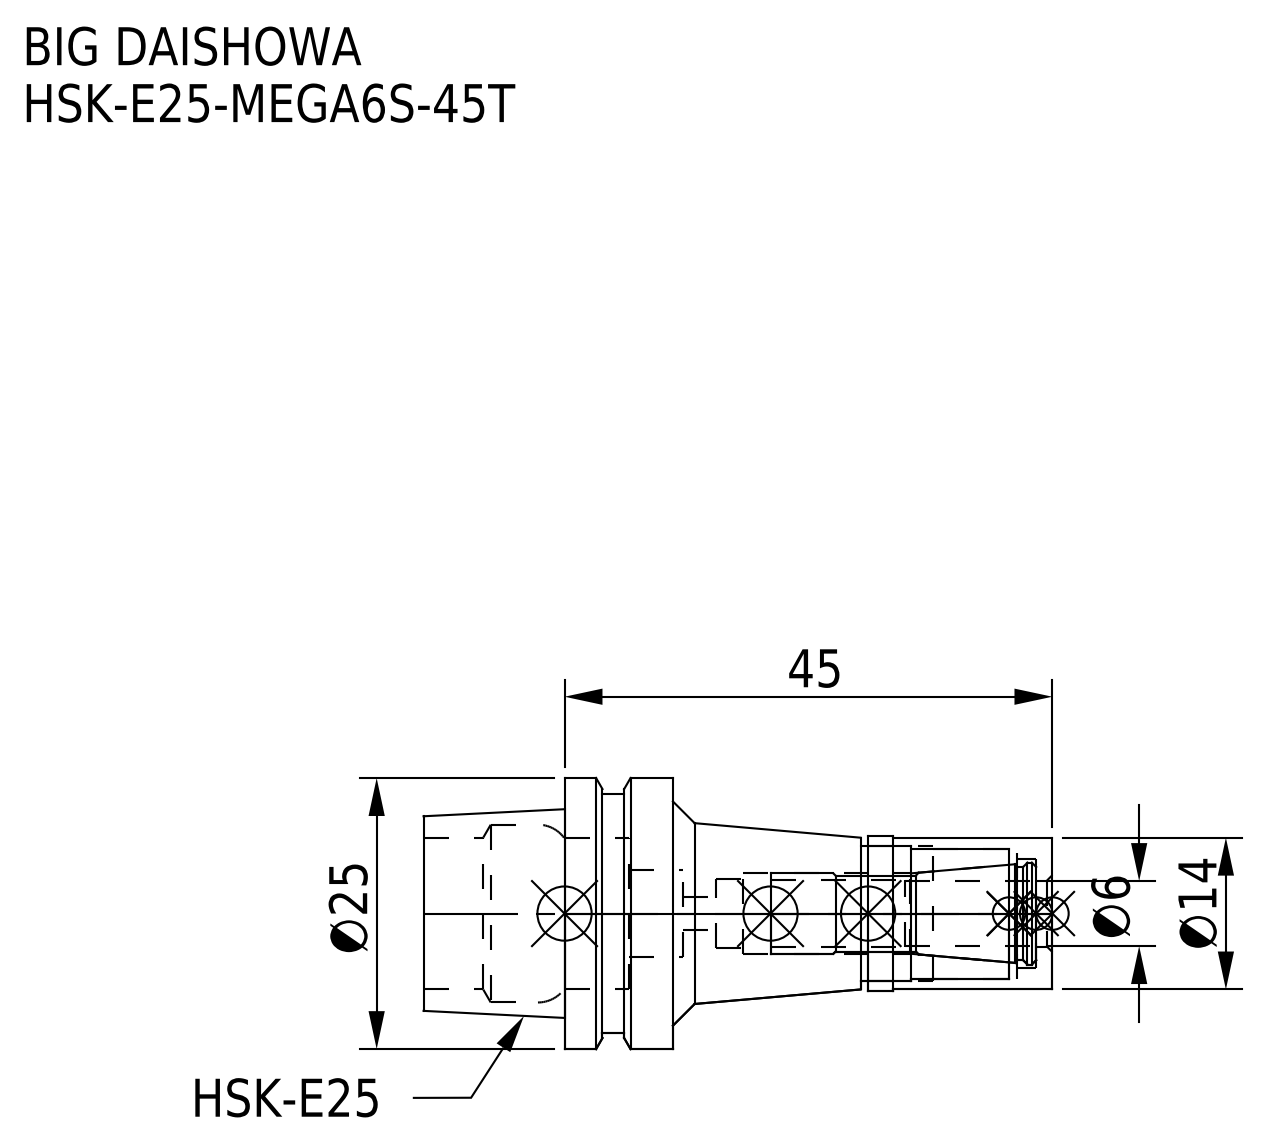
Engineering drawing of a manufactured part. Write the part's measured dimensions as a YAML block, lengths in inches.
part_name: "DXF_TEMP_ASSY_ASM_4_ASM.stp; HE25MS06045T-060_ASM.stp; HSK-E25-MEGA6S-45T-060-FreeParts; HSK-E25-MEGA6S-45T (+3 more)"
step_written_by: "SolidWorks 2019 (CONFIG_CONTROL_DESIGN)"
units: inches
bodies: {solids: 2, faces: 74, planar: 18, cylindrical: 38, other: 18}
overall_size: [2.283, 0.984, 0.984]
volume: 0.562
surface_area: 11.14
round_holes:
  - {diameter: 0.118, count: 1}
  - {diameter: 0.24, count: 1}
  - {diameter: 0.252, count: 1}
  - {diameter: 0.291, count: 1}
  - {diameter: 0.315, count: 1}
  - {diameter: 0.394, count: 1}
  - {diameter: 0.472, count: 1}
  - {diameter: 0.492, count: 1}
  - {diameter: 0.551, count: 1}
  - {diameter: 0.646, count: 1}
round_bosses_or_shafts:
  - {diameter: 0.984, count: 1}
  - {diameter: 0.866, count: 1}
  - {diameter: 0.563, count: 1}
face_to_face_distances: [0.512, 0.394, 1.772, 1.378, 1.537, 0.159, 0.234, 2.283, 0.906, 0.746]
